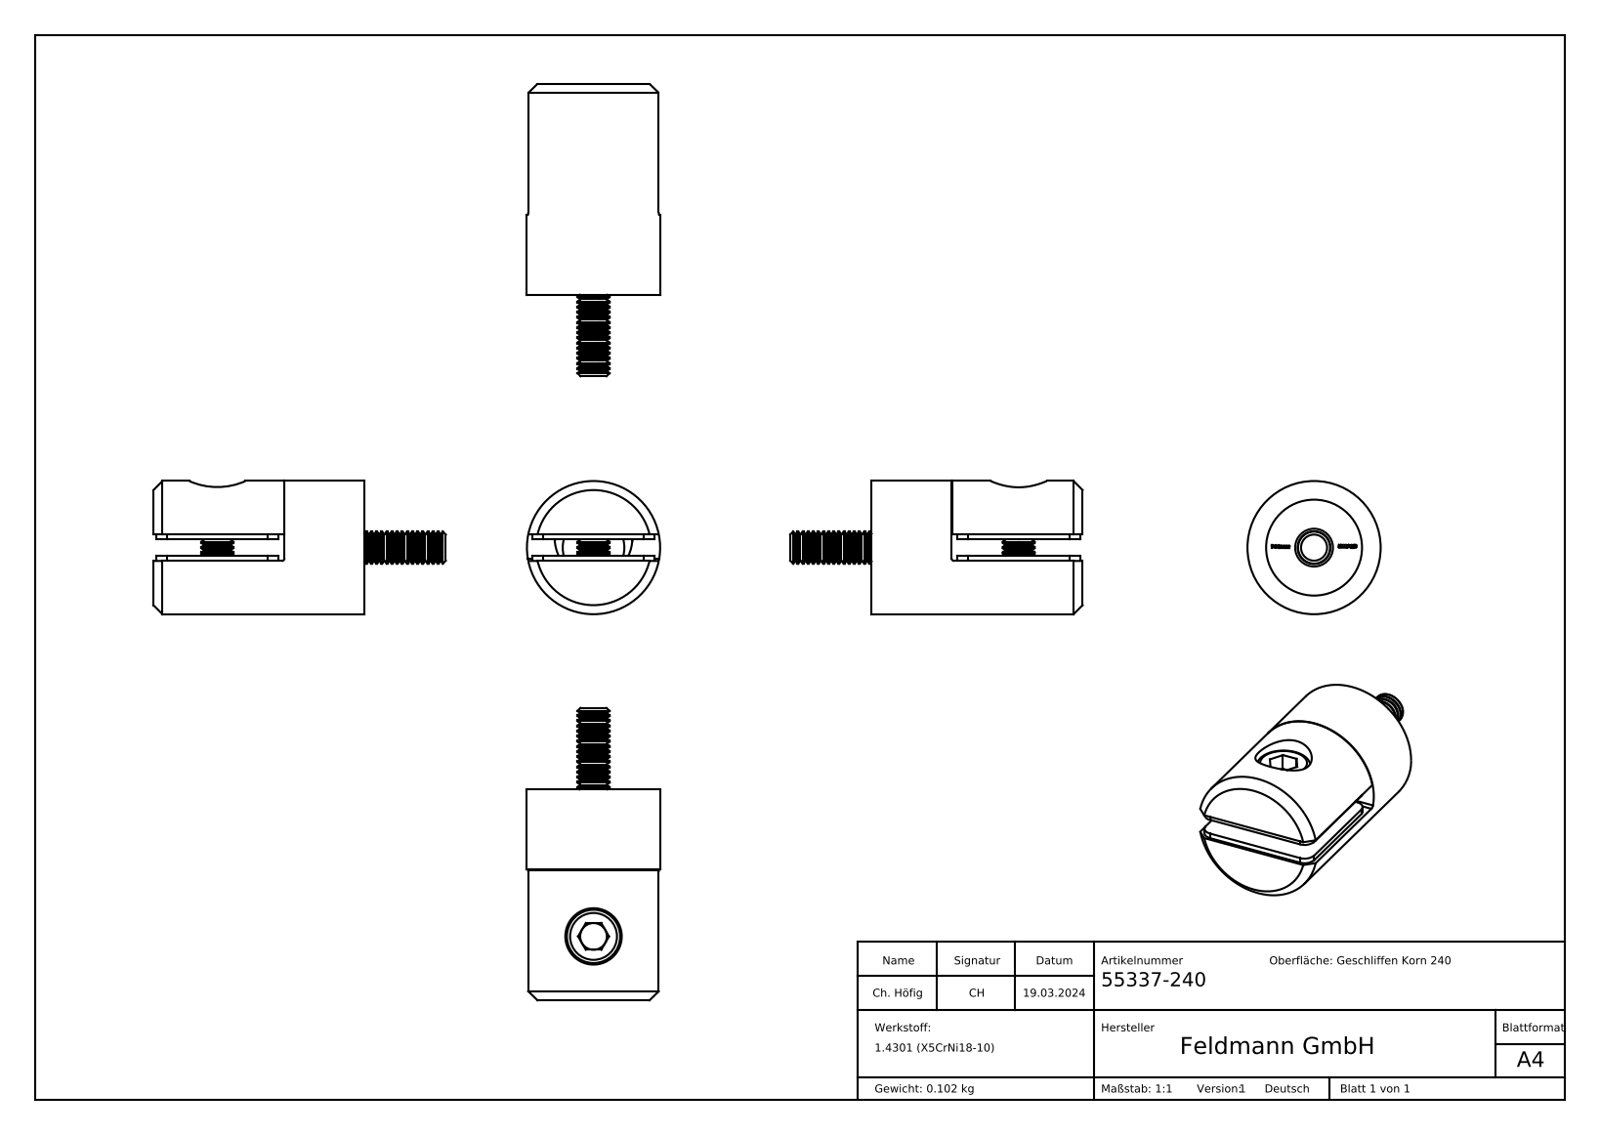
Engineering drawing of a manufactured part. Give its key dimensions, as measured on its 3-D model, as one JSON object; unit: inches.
{"part_name": "socket head cap screw_din_DIN 912 M6 x 12 --- 12S; 5533X-240 Teil1_55337-240 Teil1; 5533X-240 Teil2_5533X-240 Teil2; 5533x-240 Teil3_5533x-240 Teil3 (+2 more)", "step_written_by": "SolidWorks 2018 (CONFIG_CONTROL_DESIGN)", "units": "inches", "bodies": {"solids": 6, "faces": 708, "planar": 215, "cylindrical": 186, "other": 307}, "overall_size": [2.161, 0.984, 0.984], "volume_in3": 0.92, "surface_area_in2": 16.01, "round_holes": [[0.157, 2], [0.197, 1], [0.256, 1], [0.276, 1], [0.28, 1], [0.417, 1], [0.575, 1], [0.709, 1]], "round_bosses_or_shafts": [[0.236, 2], [0.984, 1], [0.456, 1], [0.394, 1]], "partial_cylinders_radius": [[0.008, 40], [0.079, 6], [0.049, 2], [0.02, 1]], "face_to_face_distances": [0.157, 0.039, 0.197, 0.118, 1.559, 0.201, 1.358, 0.394, 0.594, 0.965], "hole_center_spacings": [0.369, 0.472]}
